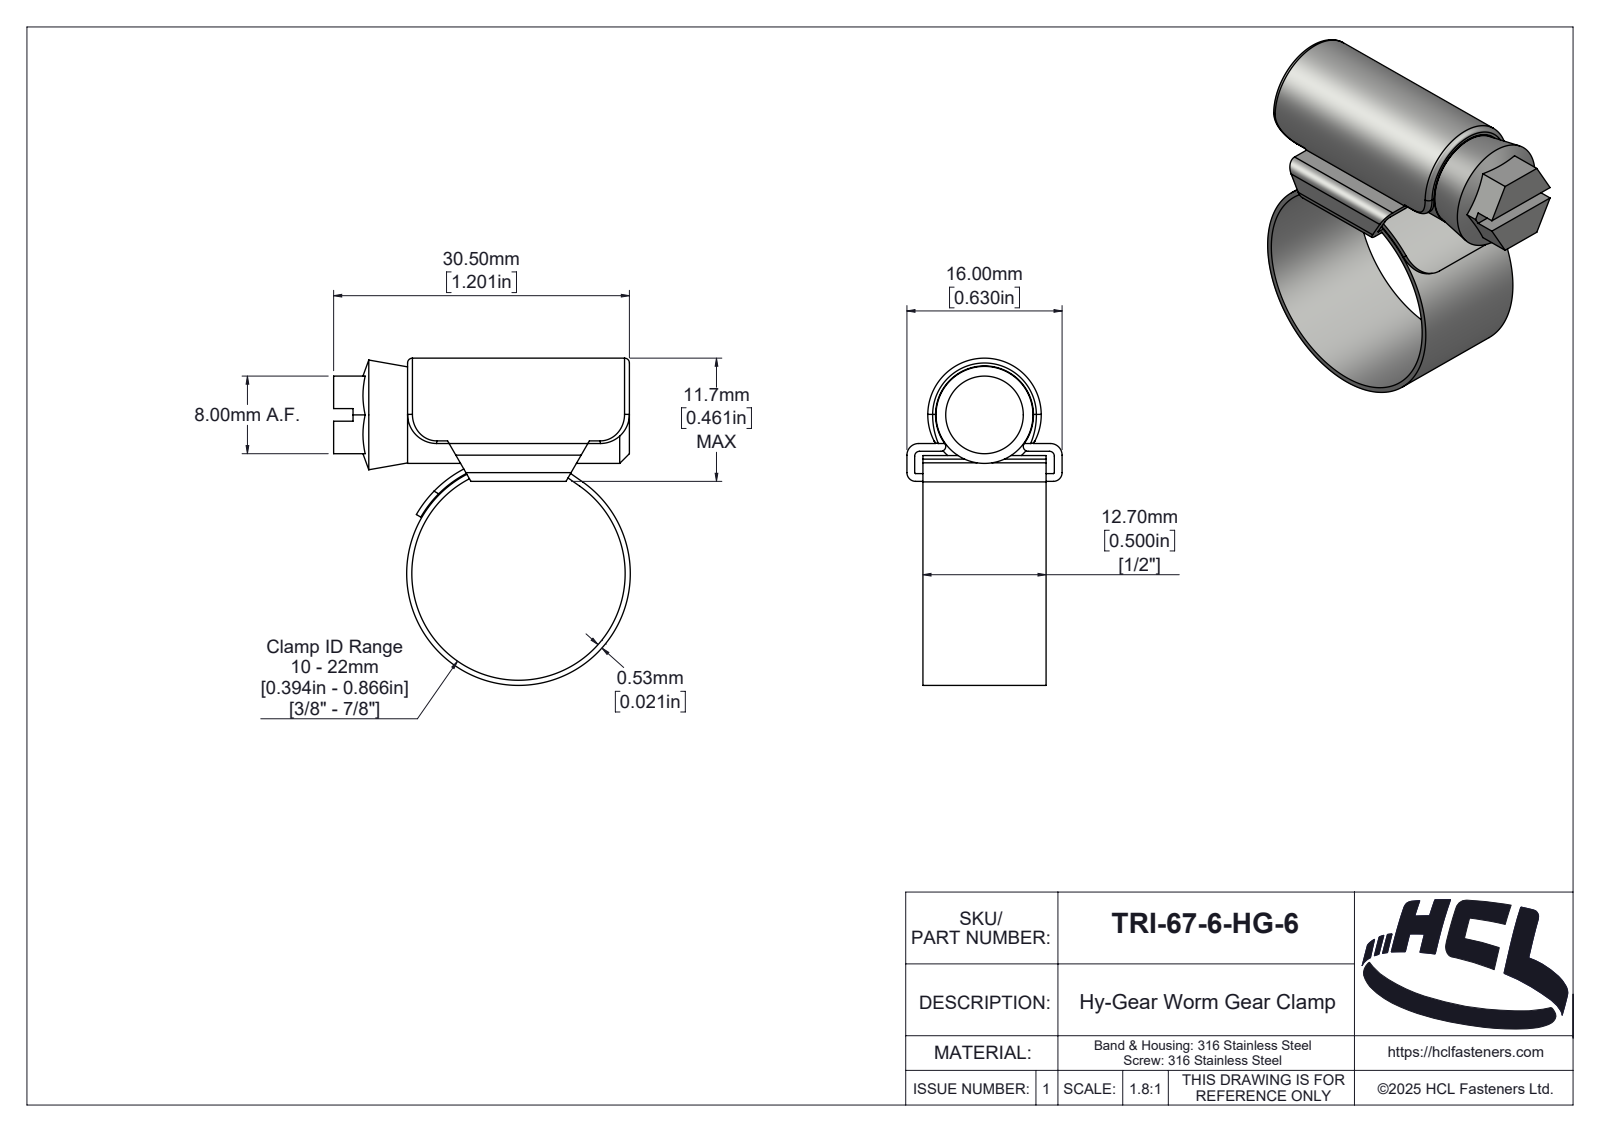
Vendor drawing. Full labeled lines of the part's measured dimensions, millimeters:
Part name (STEP PRODUCT): TRI-57-0-HG-6
STEP written by: SolidWorks 2025 (AUTOMOTIVE_DESIGN)
Units: millimetres
Bodies: 3 solids, 189 faces (39 planar, 89 cylindrical, 61 other)
Overall size (bounding box): 33.73 × 30.59 × 16
Volume: 3 553 mm³ · Surface area: 5 114 mm²
Round holes (diameter × count): ⌀22 ×1
Round bosses / shafts (diameter × count): ⌀23.06 ×1, ⌀10 ×1
Partial cylindrical surfaces — rounded edges, fillets, slot ends (radius × count): R0.5 ×6, R3 ×4, R0.1 ×2, R0.9 ×2, R1.2 ×2, R0.46 ×1, R1.89 ×1, R2 ×1
Main face-to-face distances: 0.8, 3.1, 2.3, 3.9, 30.5, 0.53, 1.65, 14.35, 12.7, 15.2
